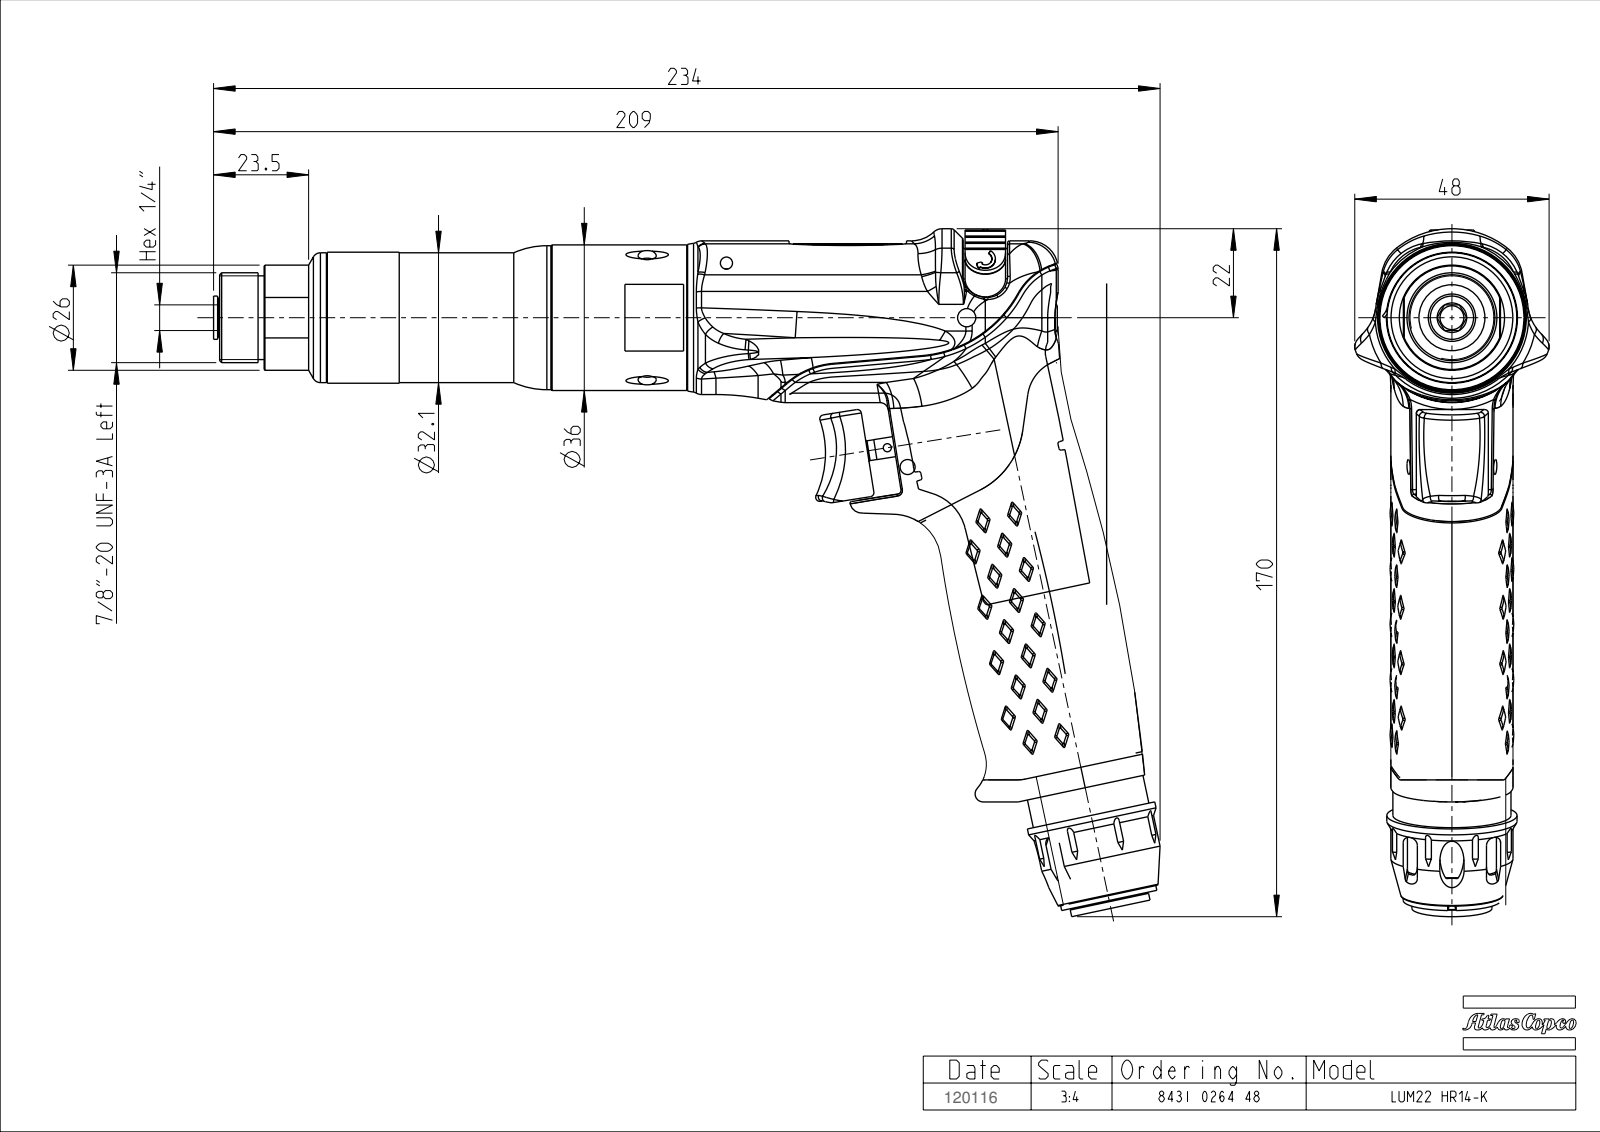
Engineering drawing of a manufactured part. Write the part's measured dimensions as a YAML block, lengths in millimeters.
part_name: "TMP16347_SW"
step_written_by: "PRO/ENGINEER BY PARAMETRIC TECHNOLOGY CORPORATION, 2008310 (CONFIG_CONTROL_DESIGN)"
units: millimeters
bodies: {solids: 0, faces: 867, planar: 151, cylindrical: 160, other: 556}
overall_size: [234.01, 170.1, 48.06]
round_holes:
  - {diameter: 4.5, count: 2}
  - {diameter: 3, count: 1}
  - {diameter: 7.3, count: 1}
  - {diameter: 7.5, count: 1}
  - {diameter: 11.4, count: 1}
  - {diameter: 11.45, count: 1}
  - {diameter: 16.3, count: 1}
  - {diameter: 26.4, count: 1}
round_bosses_or_shafts:
  - {diameter: 36, count: 1}
  - {diameter: 35.6, count: 1}
  - {diameter: 32.4, count: 1}
  - {diameter: 32.2, count: 1}
  - {diameter: 32.1, count: 1}
  - {diameter: 30.2, count: 1}
  - {diameter: 29.2, count: 1}
  - {diameter: 24.25, count: 1}
partial_cylinders:
  - {radius: 1, count: 10}
  - {radius: 0.75, count: 8}
  - {radius: 10, count: 4}
  - {radius: 38, count: 3}
  - {radius: 2.5, count: 2}
  - {radius: 3, count: 2}
  - {radius: 5, count: 2}
  - {radius: 5.5, count: 2}
face_to_face_distances: [1.5, 29.8, 32, 11, 4, 28, 2, 98.2, 27.29, 57.09]
